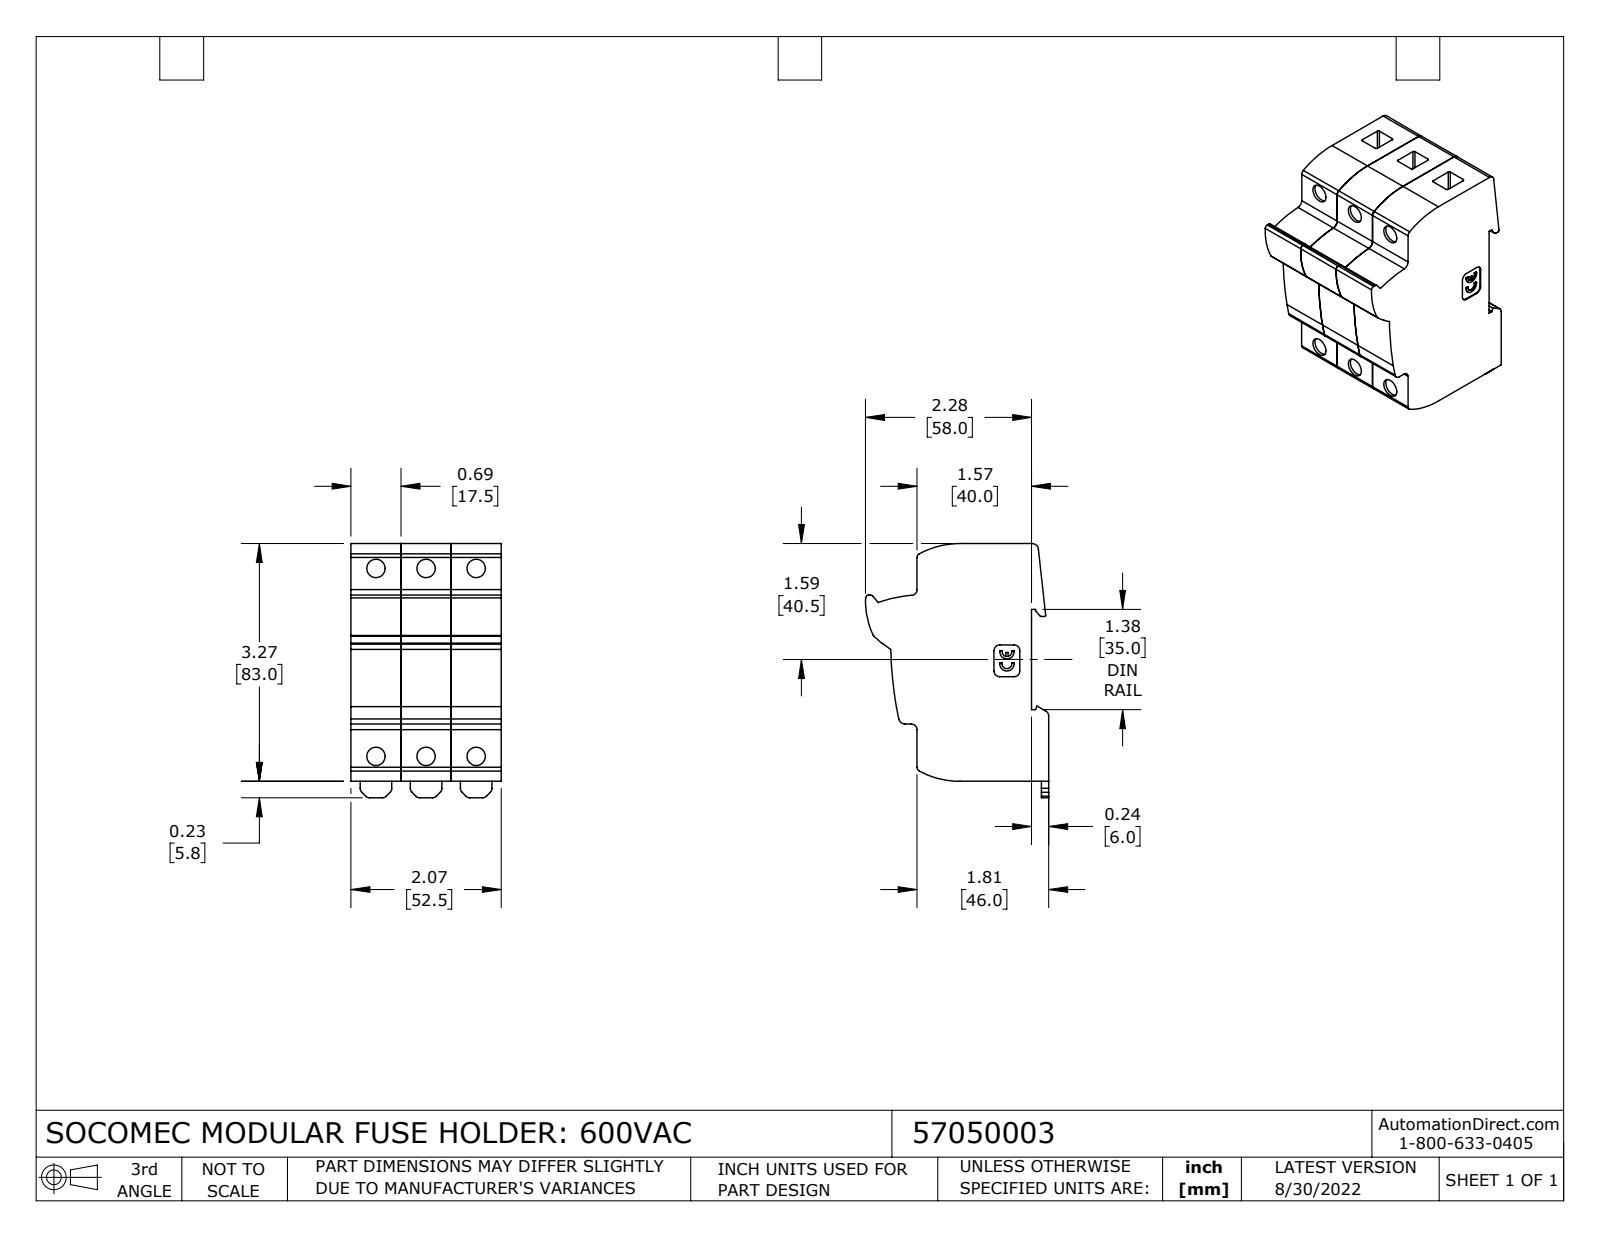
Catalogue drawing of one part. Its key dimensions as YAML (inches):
part_name: "57050003"
step_written_by: "SolidWorks 2021 (CONFIG_CONTROL_DESIGN)"
units: inches
bodies: {solids: 3, faces: 315, planar: 156, cylindrical: 159, other: 0}
overall_size: [3.496, 2.52, 2.067]
volume: 12.69
surface_area: 64
round_holes:
  - {diameter: 0.252, count: 6}
partial_cylinders:
  - {radius: 0.079, count: 19}
  - {radius: 0.02, count: 13}
  - {radius: 0.039, count: 4}
  - {radius: 0.059, count: 2}
  - {radius: 0.067, count: 2}
  - {radius: 0.087, count: 2}
  - {radius: 0.098, count: 2}
  - {radius: 1.186, count: 2}
face_to_face_distances: [0.689, 1.378, 2.067, 0.236, 1.575, 3.268, 1.811, 0.199, 0.49, 0.888]
hole_center_spacings: [0.689, 2.673, 2.583, 1.378, 2.927]
